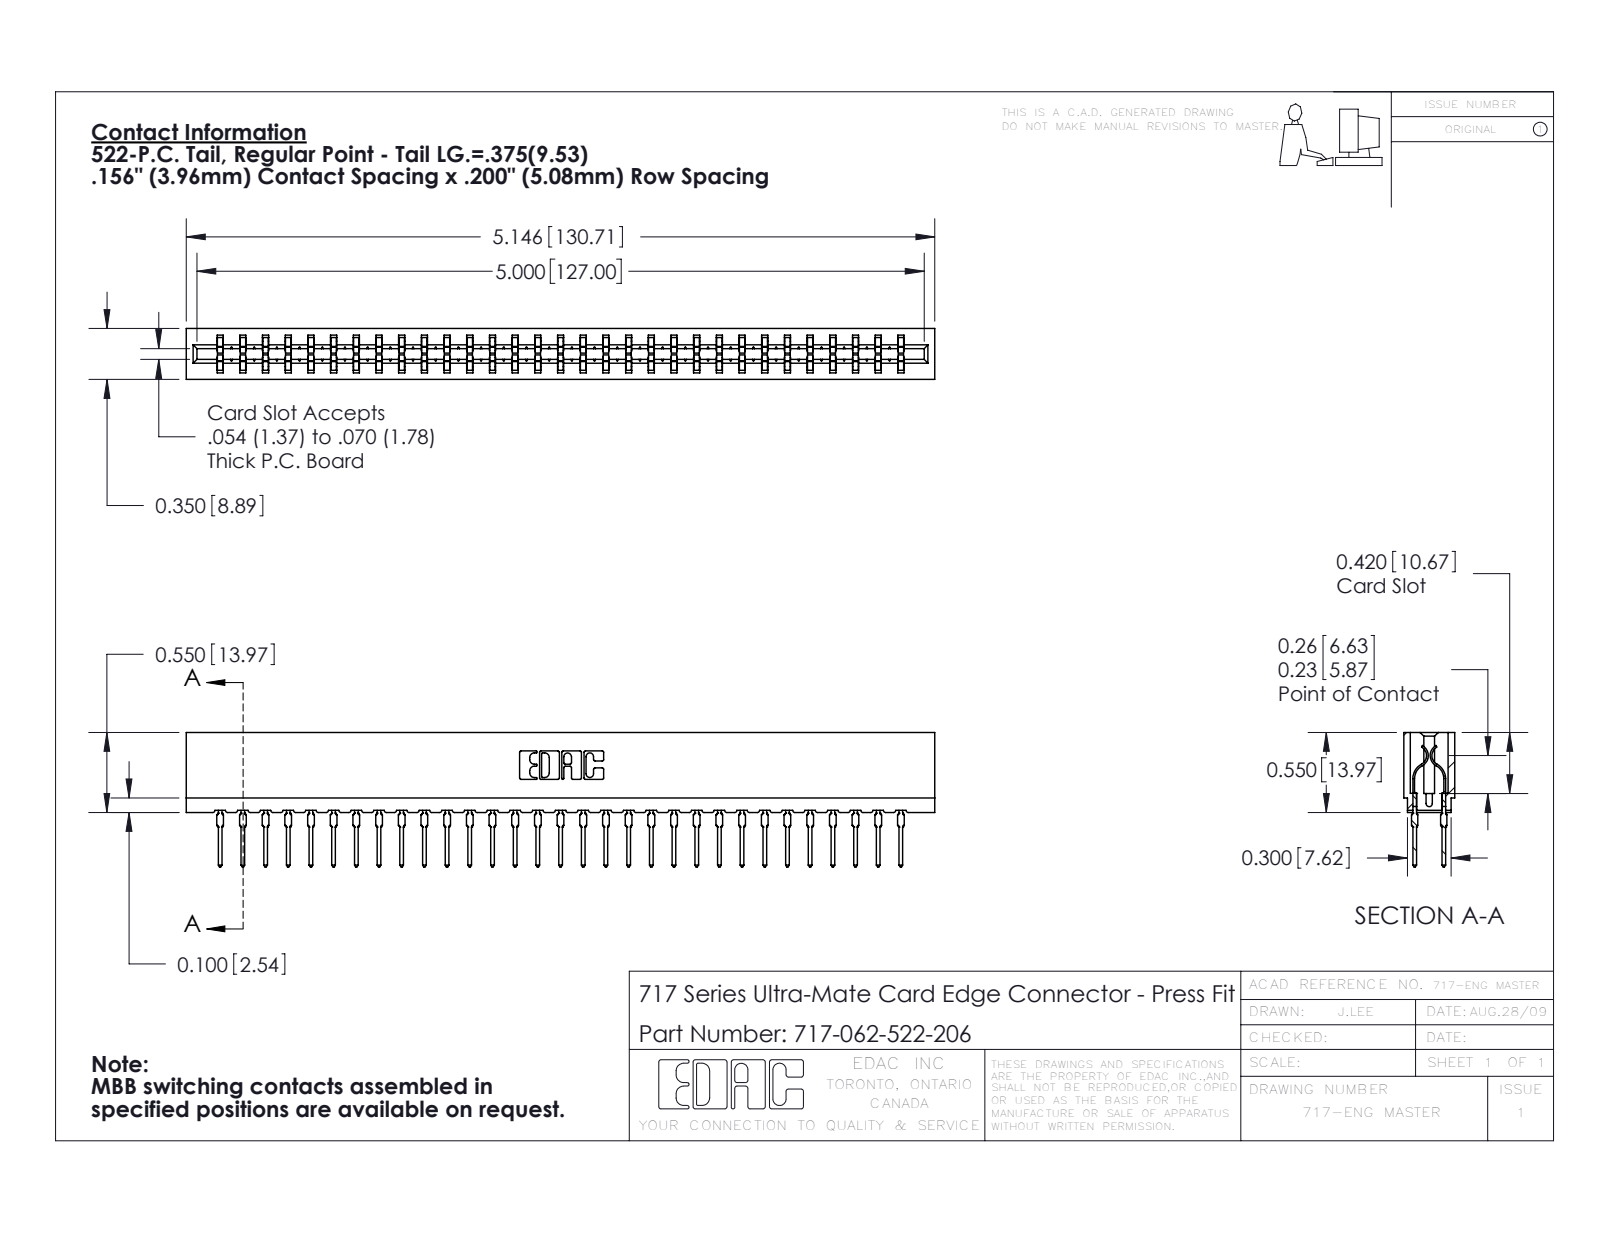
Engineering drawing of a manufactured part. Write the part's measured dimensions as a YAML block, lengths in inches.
part_name: "717 Part_Insulator Option - 06; 717-062-522-206; 745-292-001_522"
step_written_by: "SolidWorks 2016 (CONFIG_CONTROL_DESIGN)"
units: inches
bodies: {solids: 63, faces: 5674, planar: 2937, cylindrical: 1125, other: 1612}
overall_size: [5.146, 0.924, 0.35]
volume: 0.698
surface_area: 27.27
partial_cylinders:
  - {radius: 0.021, count: 124}
  - {radius: 0.015, count: 62}
  - {radius: 0.01, count: 22}
  - {radius: 0.005, count: 8}
  - {radius: 0.011, count: 8}
  - {radius: 0.007, count: 6}
  - {radius: 0.031, count: 6}
  - {radius: 0.026, count: 3}
face_to_face_distances: [0.212, 0.138, 0.35, 0.063, 0.287, 0.076, 0.149, 0.074, 0.045, 0.305]
